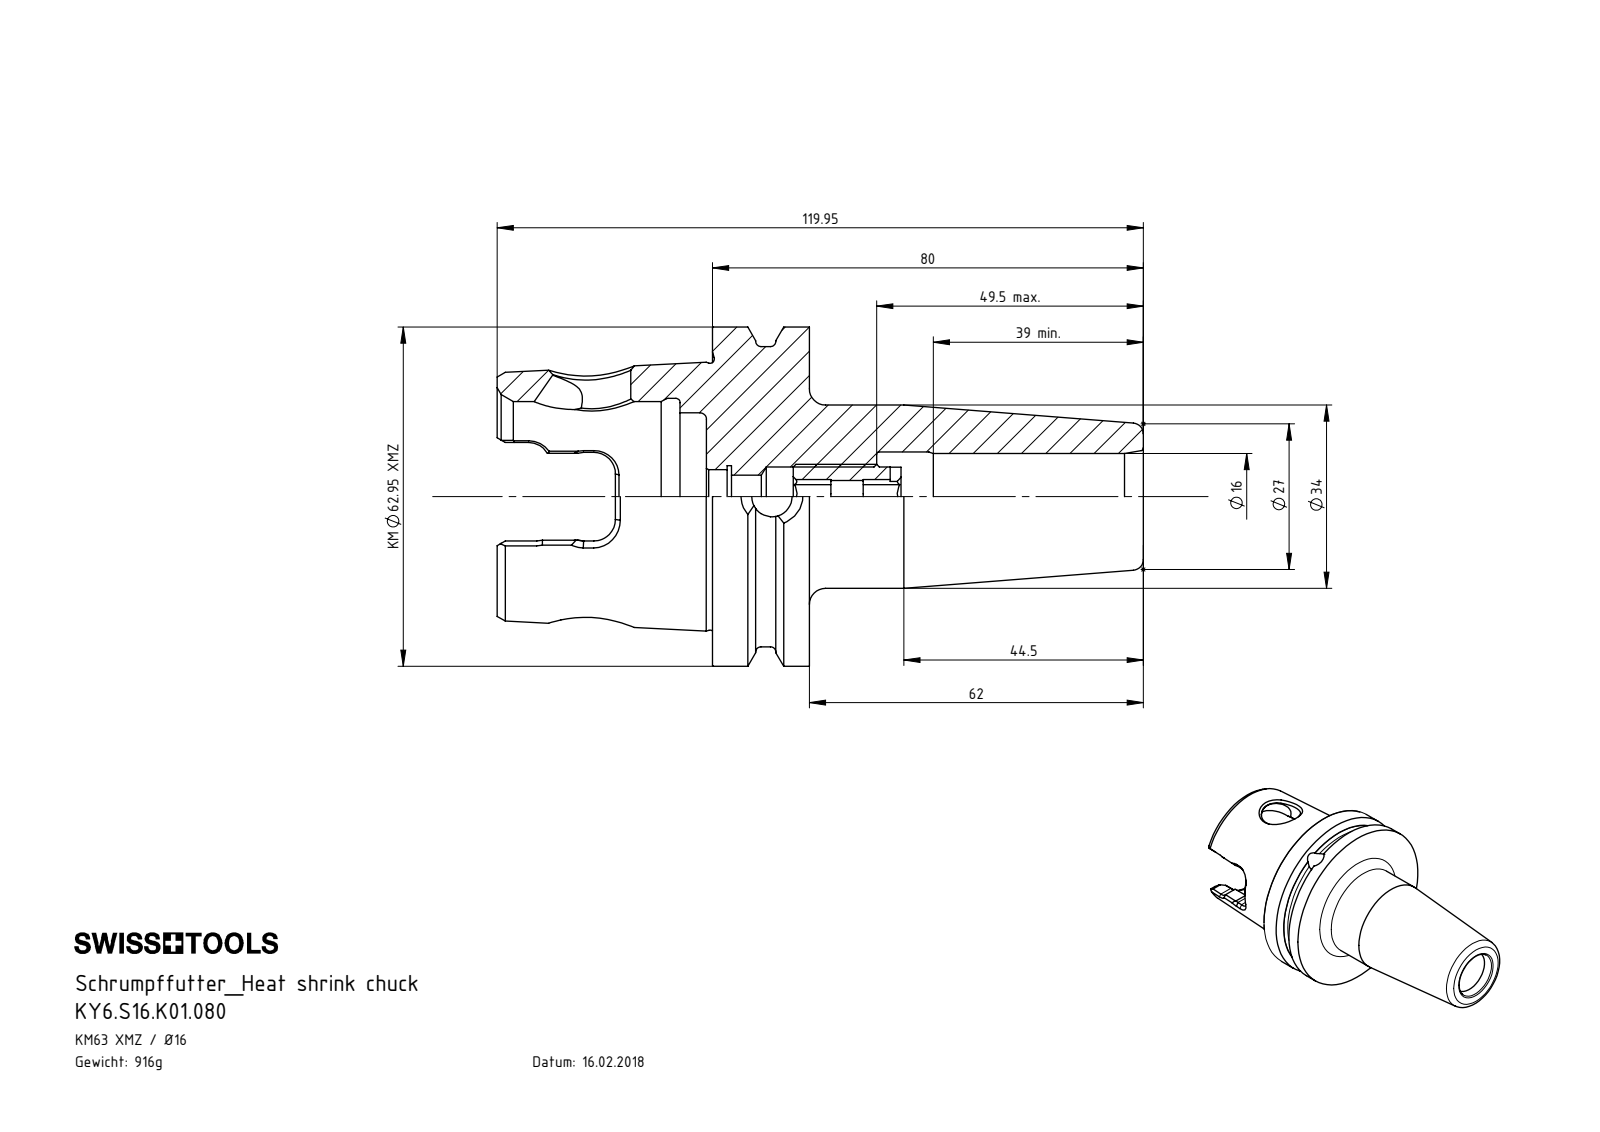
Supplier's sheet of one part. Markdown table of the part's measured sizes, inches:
| quantity | value |
| --- | --- |
| part name | KY6-S16.K01.080_A; ERU-AN5.K01.020_A; KY6.S16.K01.080 |
| STEP written by | SolidWorks 2017 (CONFIG_CONTROL_DESIGN) |
| units | inches |
| bodies | 2 solids, 277 faces (79 planar, 60 cylindrical, 138 other) |
| overall size | 4.722 × 2.478 × 2.478 |
| volume | 7.122 in³ |
| surface area | 46.53 in² |
| round holes (diameter × count) | 0.294 × 2, 0.236 × 1, 0.315 × 1, 0.334 × 1, 0.394 × 1, 0.433 × 1, 0.453 × 1, 0.571 × 1, 0.63 × 1, 0.654 × 1, 1.224 × 1, 1.389 × 1 |
| round bosses / shafts (diameter × count) | 2.478 × 1, 2.193 × 1, 1.339 × 1, 0.472 × 1 |
| partial cylindrical surfaces (radius × count) | 0.157 × 6, 0.277 × 2 |
| main face-to-face distances | 0.709, 0.043, 0.752, 0.236, 0.193, 0.945, 1.337, 1.53, 1.573, 2.281 |
